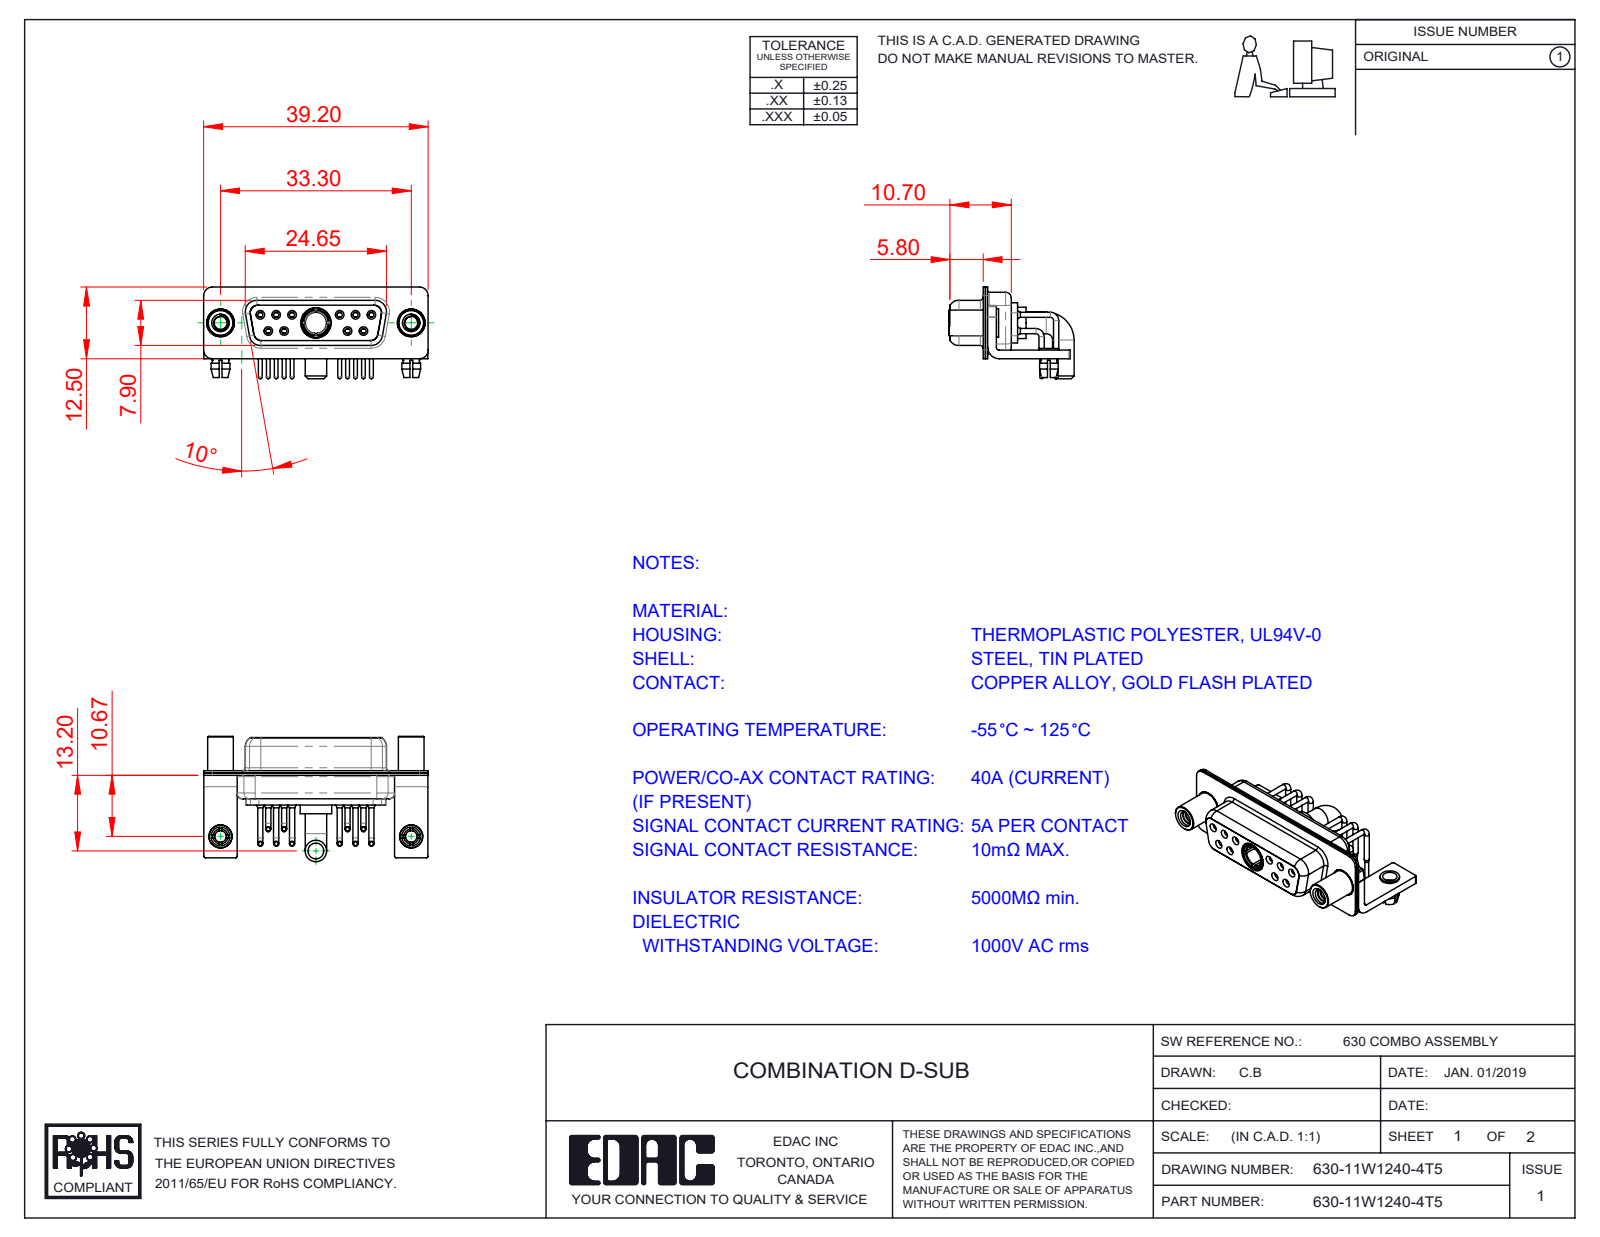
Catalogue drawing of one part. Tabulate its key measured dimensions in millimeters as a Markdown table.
| quantity | value |
| --- | --- |
| part name | 630Combo Stabilizer Bracket; 630Combo Contact Row 1; Power Socket_40A RA; 630Combo Shell Front_15 Contacts (+6 more) |
| STEP written by | SolidWorks 2020 (CONFIG_CONTROL_DESIGN) |
| units | millimeters |
| bodies | 21 solids, 1067 faces (316 planar, 484 cylindrical, 267 other) |
| overall size | 39.2 × 21.88 × 16 |
| volume | 3 152 mm³ |
| surface area | 7 441 mm² |
| round holes (diameter × count) | 2 × 12, 0.9 × 10, 1.1 × 10, 1.5 × 10, 1.7 × 6, 1.6 × 4, 4.85 × 3, 2.26 × 2, 2.5 × 2, 3.2 × 2, 4 × 2, 4.05 × 2 |
| round bosses / shafts (diameter × count) | 0.9 × 10, 0.65 × 10, 1.6 × 6, 5 × 2, 4.95 × 2, 4.8 × 2, 4.5 × 2, 4 × 2 |
| partial cylindrical surfaces (radius × count) | 0.25 × 16, 1.5 × 16, 2 × 13, 1.35 × 12, 1.6 × 8, 0.5 × 5, 0.6 × 4, 0.65 × 4 |
| main face-to-face distances | 0.4, 0.8, 0.45, 1.4, 8.45, 1.8, 1.5, 8.9, 6.2, 2.3 |
| hole center spacings | 3.16, 2.77, 13.85, 11.08, 16.62, 5.03, 5.04, 5.54 |
